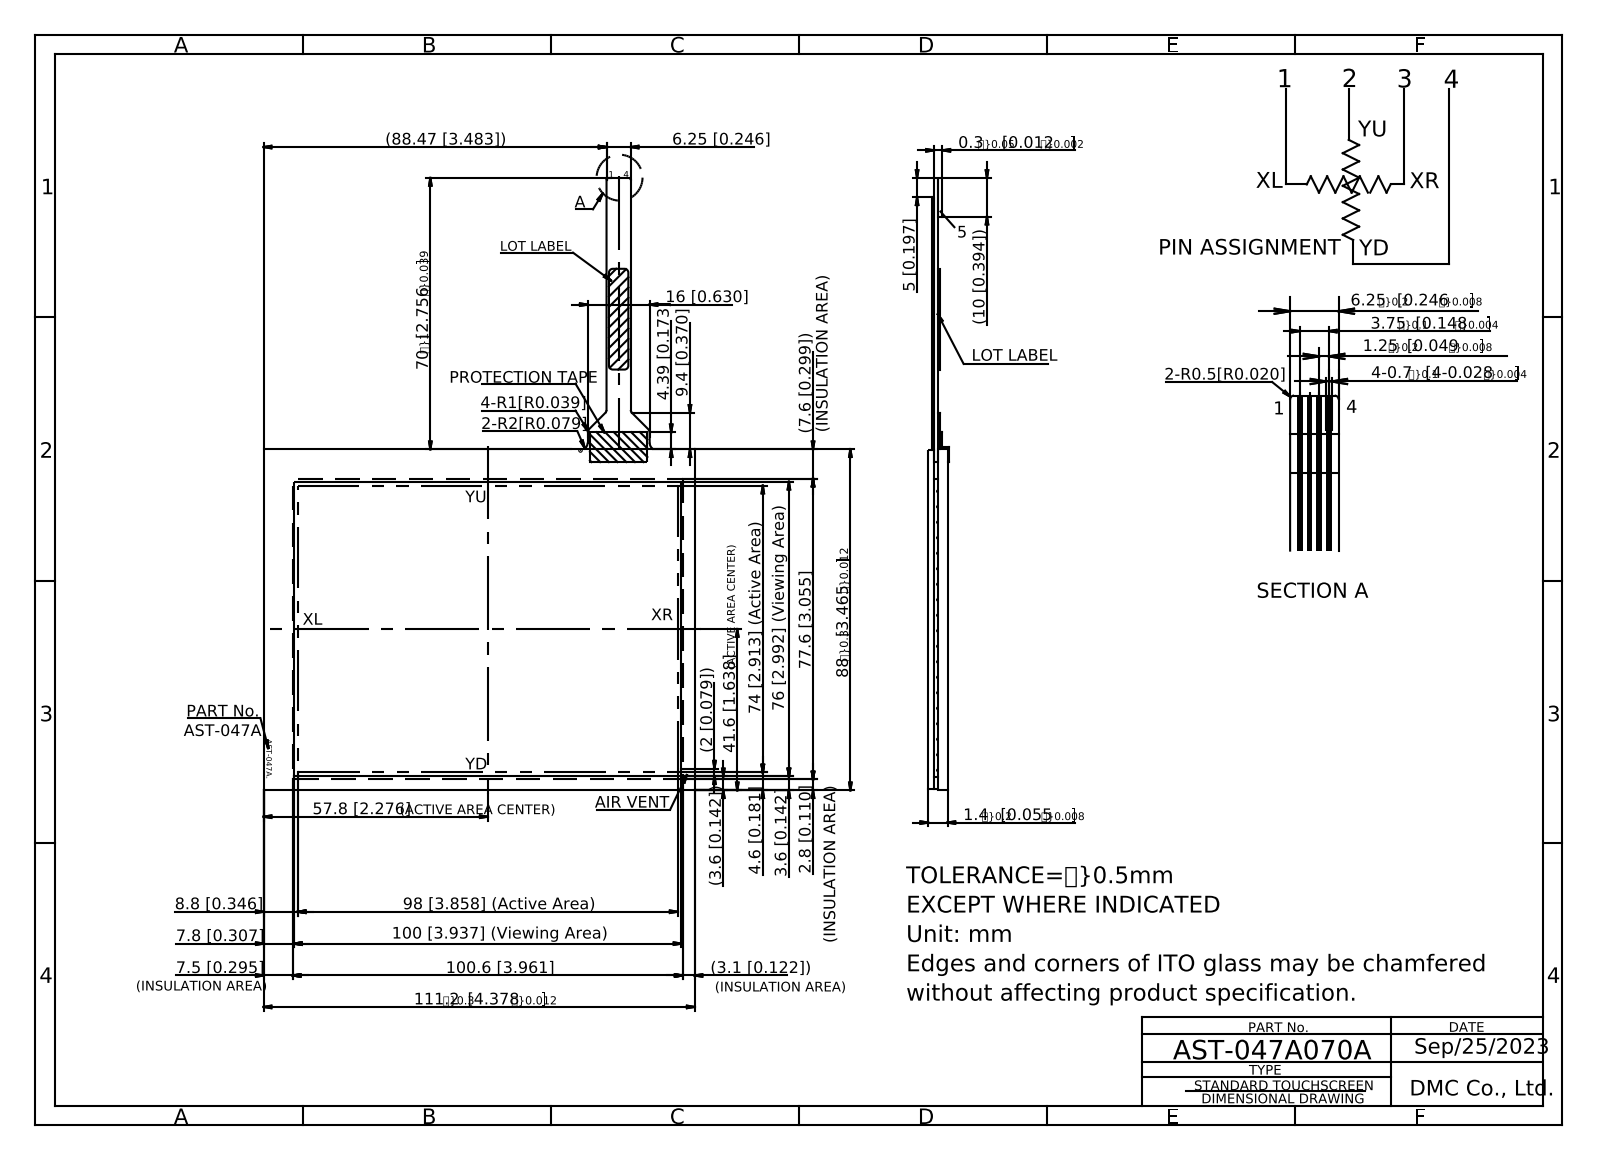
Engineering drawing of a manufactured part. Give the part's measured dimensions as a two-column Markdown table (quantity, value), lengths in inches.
| quantity | value |
| --- | --- |
| part name | AST-047A070A |
| STEP written by | Autodesk Inventor 2020 (CONFIG_CONTROL_DESIGN) |
| units | inches |
| bodies | 1 solid, 51 faces (45 planar, 6 cylindrical, 0 other) |
| overall size | 6.913 × 6.129 × 0.055 |
| volume | 0.838 in³ |
| surface area | 32.91 in² |
| partial cylindrical surfaces (radius × count) | 0.039 × 4, 0.02 × 2 |
| main face-to-face distances | 0.055, 0.047, 0.043, 0.051, 3.465, 4.378, 0.031, 0.016, 0.02, 0.024 |
